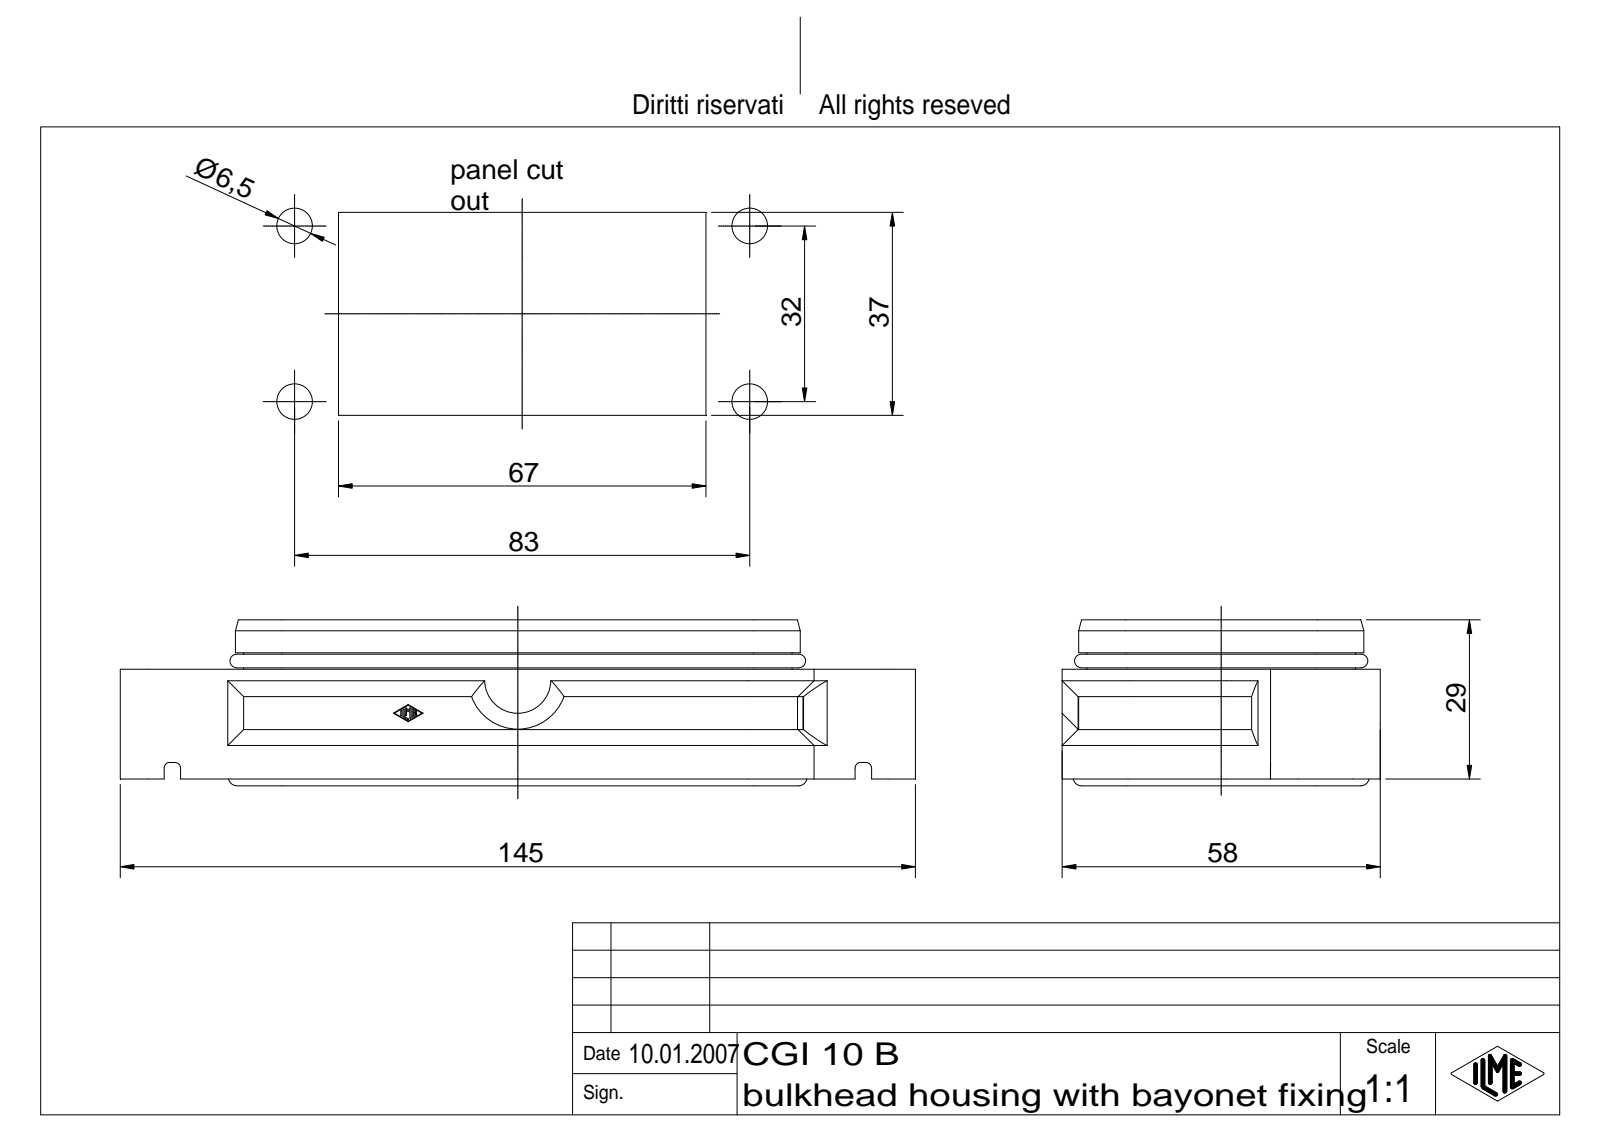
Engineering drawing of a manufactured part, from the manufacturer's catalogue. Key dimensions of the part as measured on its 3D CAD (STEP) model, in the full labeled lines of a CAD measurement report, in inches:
Part name (STEP PRODUCT): Anbaugehäuse
STEP written by: Autodesk Inventor 7 (AUTOMOTIVE_DESIGN)
Units: inches
Bodies: 1 solid, 360 faces (176 planar, 134 cylindrical, 50 other)
Overall size (bounding box): 5.709 × 2.283 × 1.191
Volume: 3.872 in³ · Surface area: 53.75 in²
Round holes (diameter × count): ⌀0.217 ×4, ⌀0.128 ×2
Round bosses / shafts (diameter × count): ⌀0.098 ×4, ⌀0.118 ×2
Partial cylindrical surfaces — rounded edges, fillets, slot ends (radius × count): R0.004 ×14, R0.197 ×8, R0.276 ×6, R0.039 ×4, R0.128 ×4, R0.256 ×4, R0.335 ×4, R0.374 ×4
Main face-to-face distances: 0.256, 0.118, 1.772, 2.028, 0.787, 0.138, 1.909, 0.354, 2.165, 0.217
Hole centre spacings: 0.631, 3.289, 1.26, 3.268, 3.502, 3.189
